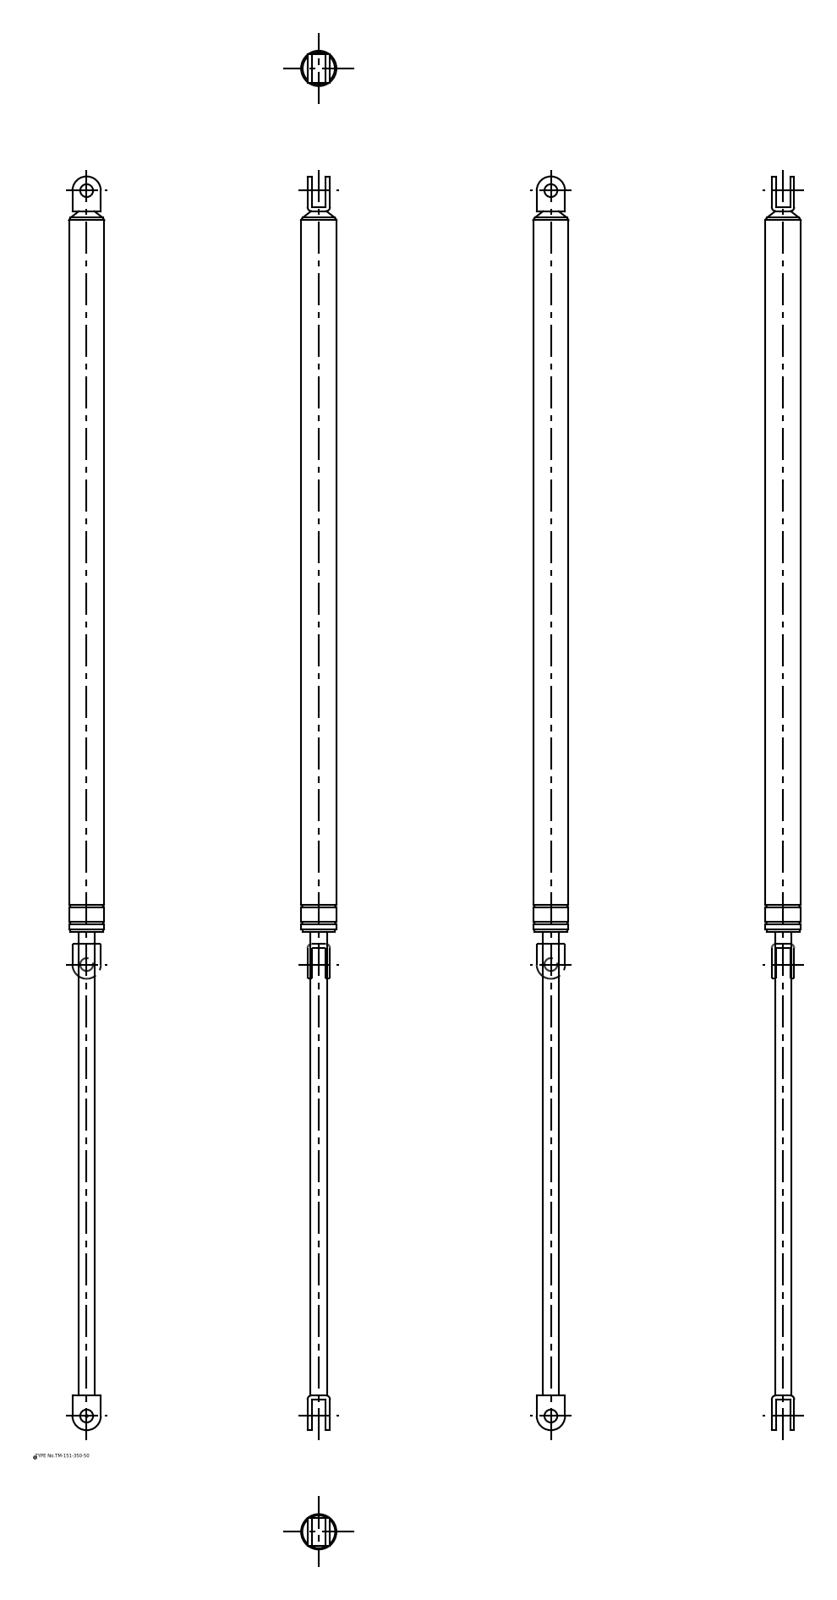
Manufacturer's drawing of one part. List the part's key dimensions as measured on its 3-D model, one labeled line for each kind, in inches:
Part name (STEP PRODUCT): TM_151_350_50; TM_151_350_50_div
STEP written by: spGate 16.7.1 (AUTOMOTIVE_DESIGN)
Units: inches
Bodies: 2 solids, 64 faces (22 planar, 32 cylindrical, 10 other)
Overall size (bounding box): 38.268 × 1.11 × 1.11
Volume: 23.15 in³ · Surface area: 106.9 in²
Round holes (diameter × count): ⌀0.394 ×2
Round bosses / shafts (diameter × count): ⌀1.11 ×1, ⌀1.079 ×1, ⌀1.004 ×1, ⌀0.492 ×1
Partial cylindrical surfaces — rounded edges, fillets, slot ends (radius × count): R0.126 ×4, R0.433 ×2
Main face-to-face distances: 0.126, 0.559, 0.685, 0.433, 0.866, 36.268, 14.26, 36.394, 22.134, 22.008
Hole centre spacings: 37.402
